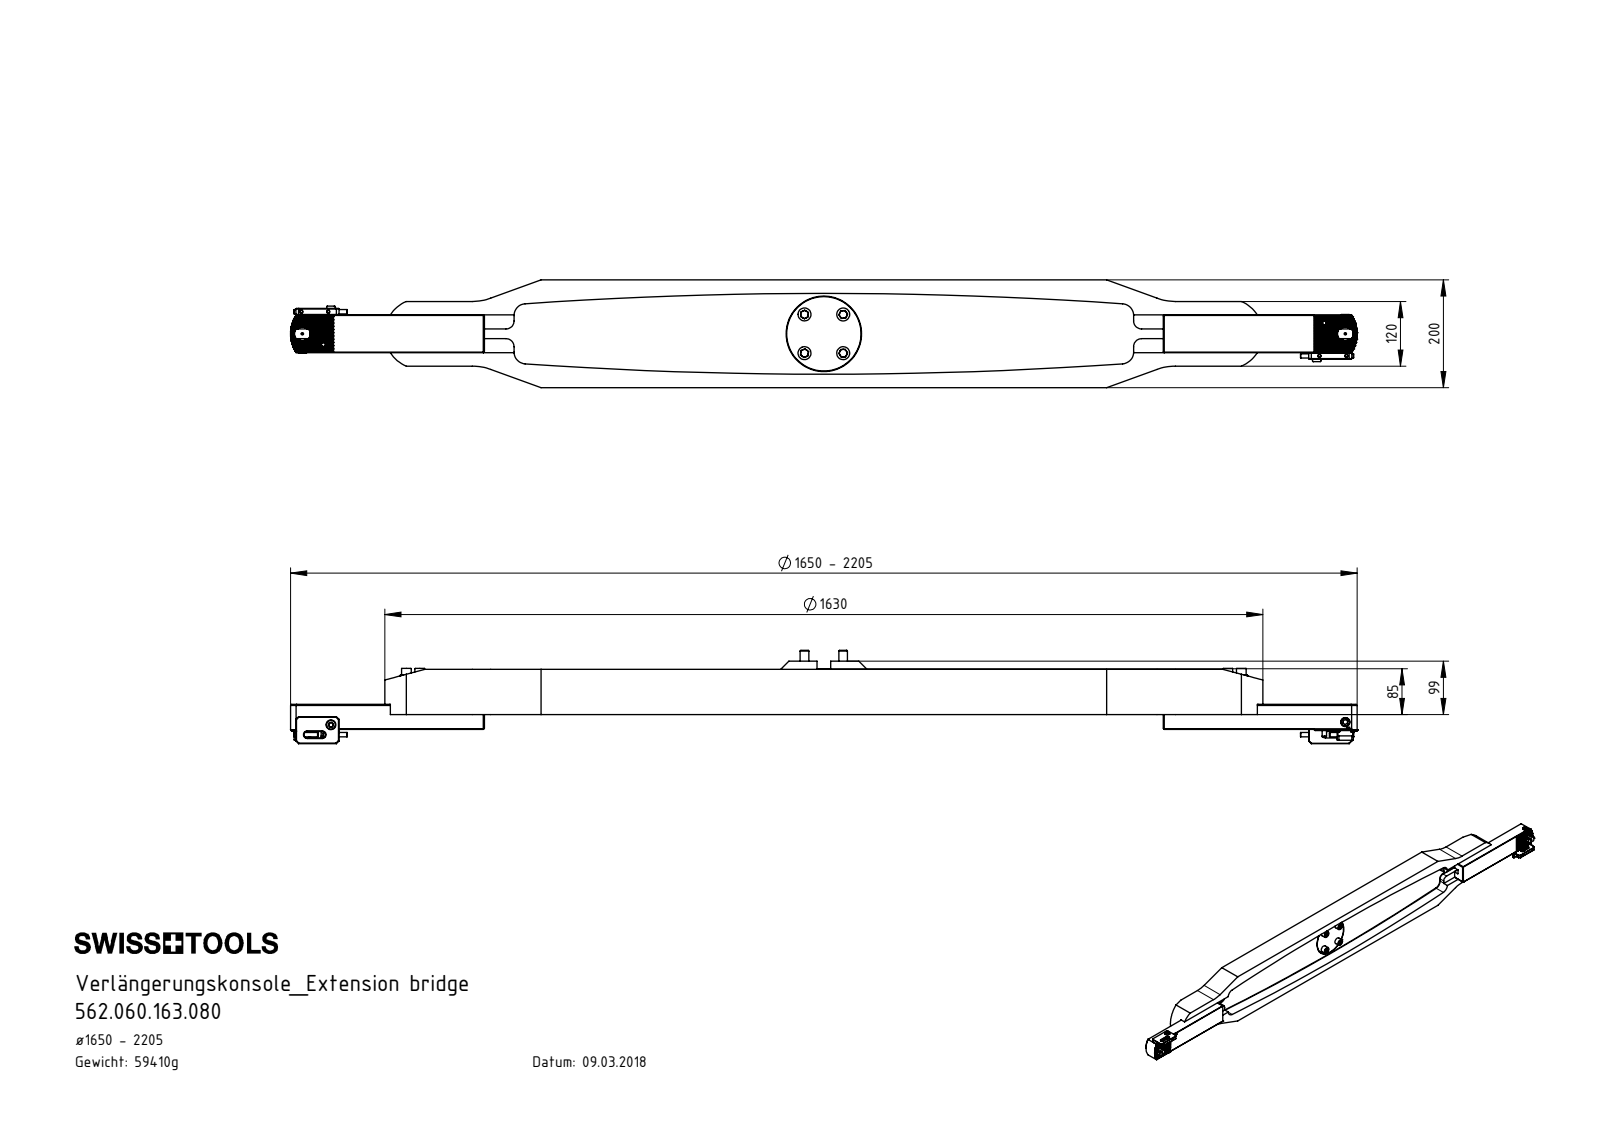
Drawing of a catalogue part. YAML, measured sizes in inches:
part_name: "562.060.163.080; VK3-VK1.360.048; ISO 4026 - M8 x 45; ISO 4762 - M10 x 16 (+8 more)"
step_written_by: "SolidWorks 2017 (CONFIG_CONTROL_DESIGN)"
units: inches
bodies: {solids: 46, faces: 2145, planar: 916, cylindrical: 736, other: 493}
overall_size: [77.953, 7.874, 6.811]
volume: 1042
surface_area: 2320
round_holes:
  - {diameter: 0.709, count: 42}
  - {diameter: 0.402, count: 40}
  - {diameter: 0.512, count: 16}
  - {diameter: 0.197, count: 4}
  - {diameter: 0.236, count: 4}
  - {diameter: 0.268, count: 4}
  - {diameter: 0.472, count: 4}
  - {diameter: 0.669, count: 4}
  - {diameter: 0.079, count: 2}
  - {diameter: 0.315, count: 2}
  - {diameter: 0.335, count: 2}
  - {diameter: 0.413, count: 2}
round_bosses_or_shafts:
  - {diameter: 0.945, count: 12}
  - {diameter: 0.63, count: 8}
  - {diameter: 0.472, count: 4}
  - {diameter: 0.394, count: 2}
  - {diameter: 0.315, count: 2}
  - {diameter: 5.433, count: 1}
partial_cylinders:
  - {radius: 0.006, count: 33}
  - {radius: 0.079, count: 22}
  - {radius: 0.866, count: 12}
  - {radius: 0.591, count: 6}
  - {radius: 0.059, count: 4}
  - {radius: 0.217, count: 4}
  - {radius: 0.236, count: 4}
  - {radius: 0.315, count: 4}
face_to_face_distances: [1.26, 2.559, 0.512, 1.772, 2.795, 3.307, 1.535, 7.874, 1.575, 5.315]
hole_center_spacings: [0.984, 1.857, 1.969, 2.521, 1.575, 2.953, 3.346, 57.087]
